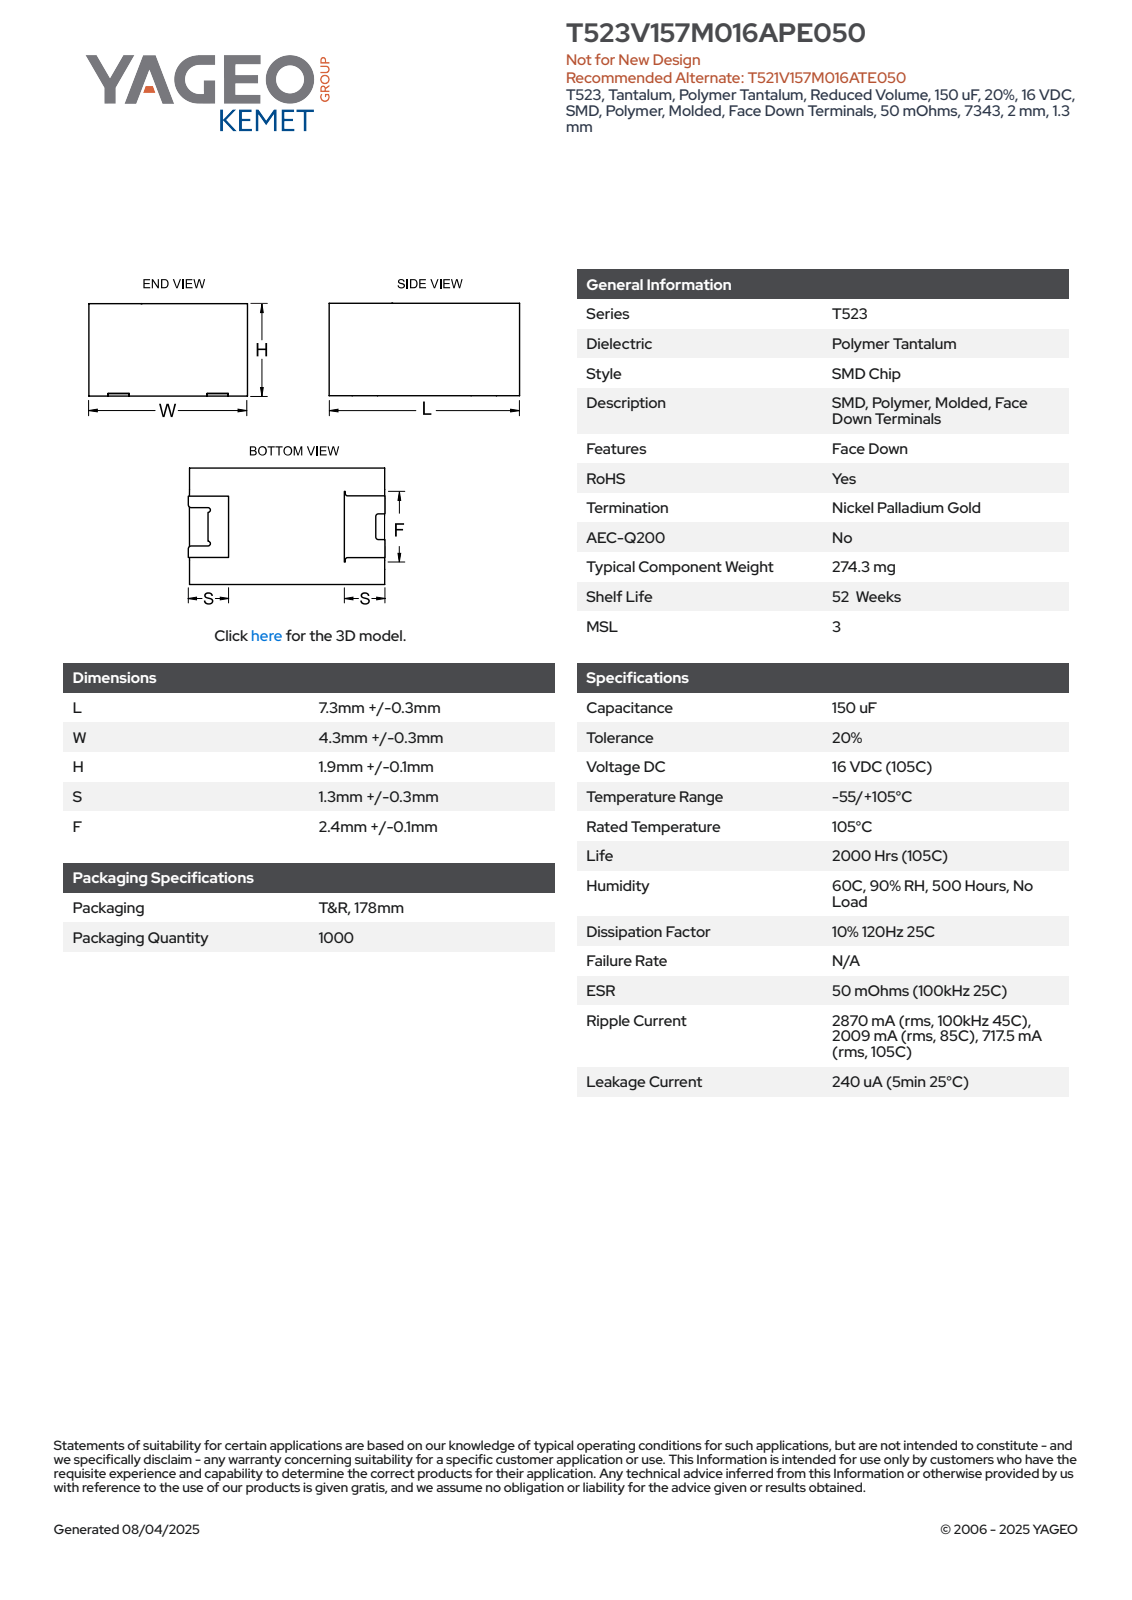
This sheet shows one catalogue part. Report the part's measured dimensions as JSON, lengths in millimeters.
{"part_name": "CTS_TFD_JVW_7343_L7.6W4.6H2S1.3F2.5", "step_written_by": "SolidWorks 2020 (AUTOMOTIVE_DESIGN)", "units": "millimeters", "bodies": {"solids": 1, "faces": 88, "planar": 86, "cylindrical": 2, "other": 0}, "overall_size": [7.62, 4.6, 2.02], "volume_mm3": 70, "surface_area_mm2": 119, "partial_cylinders_radius": [[0.15, 2]], "face_to_face_distances": [2, 4.6, 7.6, 2.01, 2.02, 7.61, 7.62, 1, 1.67, 2.93]}
